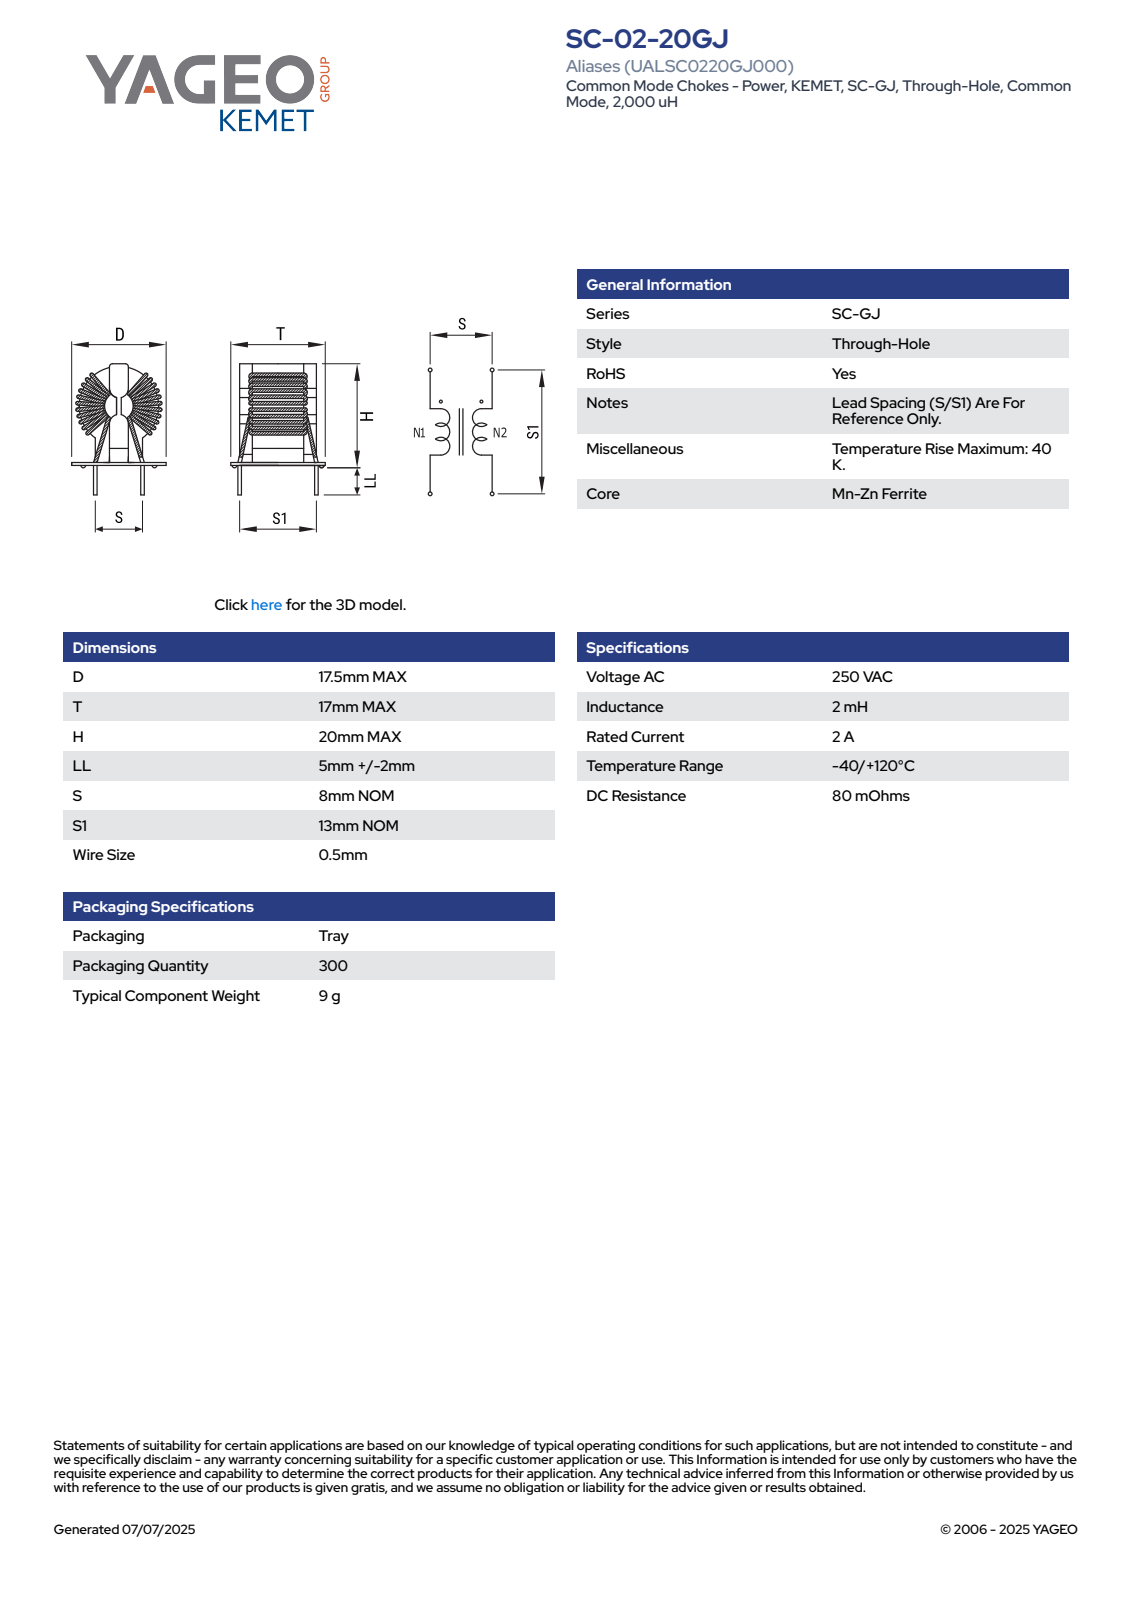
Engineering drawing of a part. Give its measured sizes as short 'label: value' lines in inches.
name: SC-02-20GJ
written by: SolidWorks 2018 (AUTOMOTIVE_DESIGN)
unit: in
bodies: 4 solids, 395 faces (167 planar, 128 cylindrical, 100 other)
size: 0.984 × 0.689 × 0.669
volume: 0.216 in³; area: 5.554 in²
holes: 1× ⌀0.287, 1× ⌀0.504
bosses: 8× ⌀0.02, 1× ⌀0.547, 1× ⌀0.285
rounds: 20× R0.02, 16× R0.01, 6× R0.008, 4× R0.039, 4× R0.063, 3× R0.012, 2× R0.035, 2× R0.079
face distances: 0.055, 0.079, 0.393, 0.126, 0.041, 0.047, 0.433, 0.119, 0.314, 0.393
